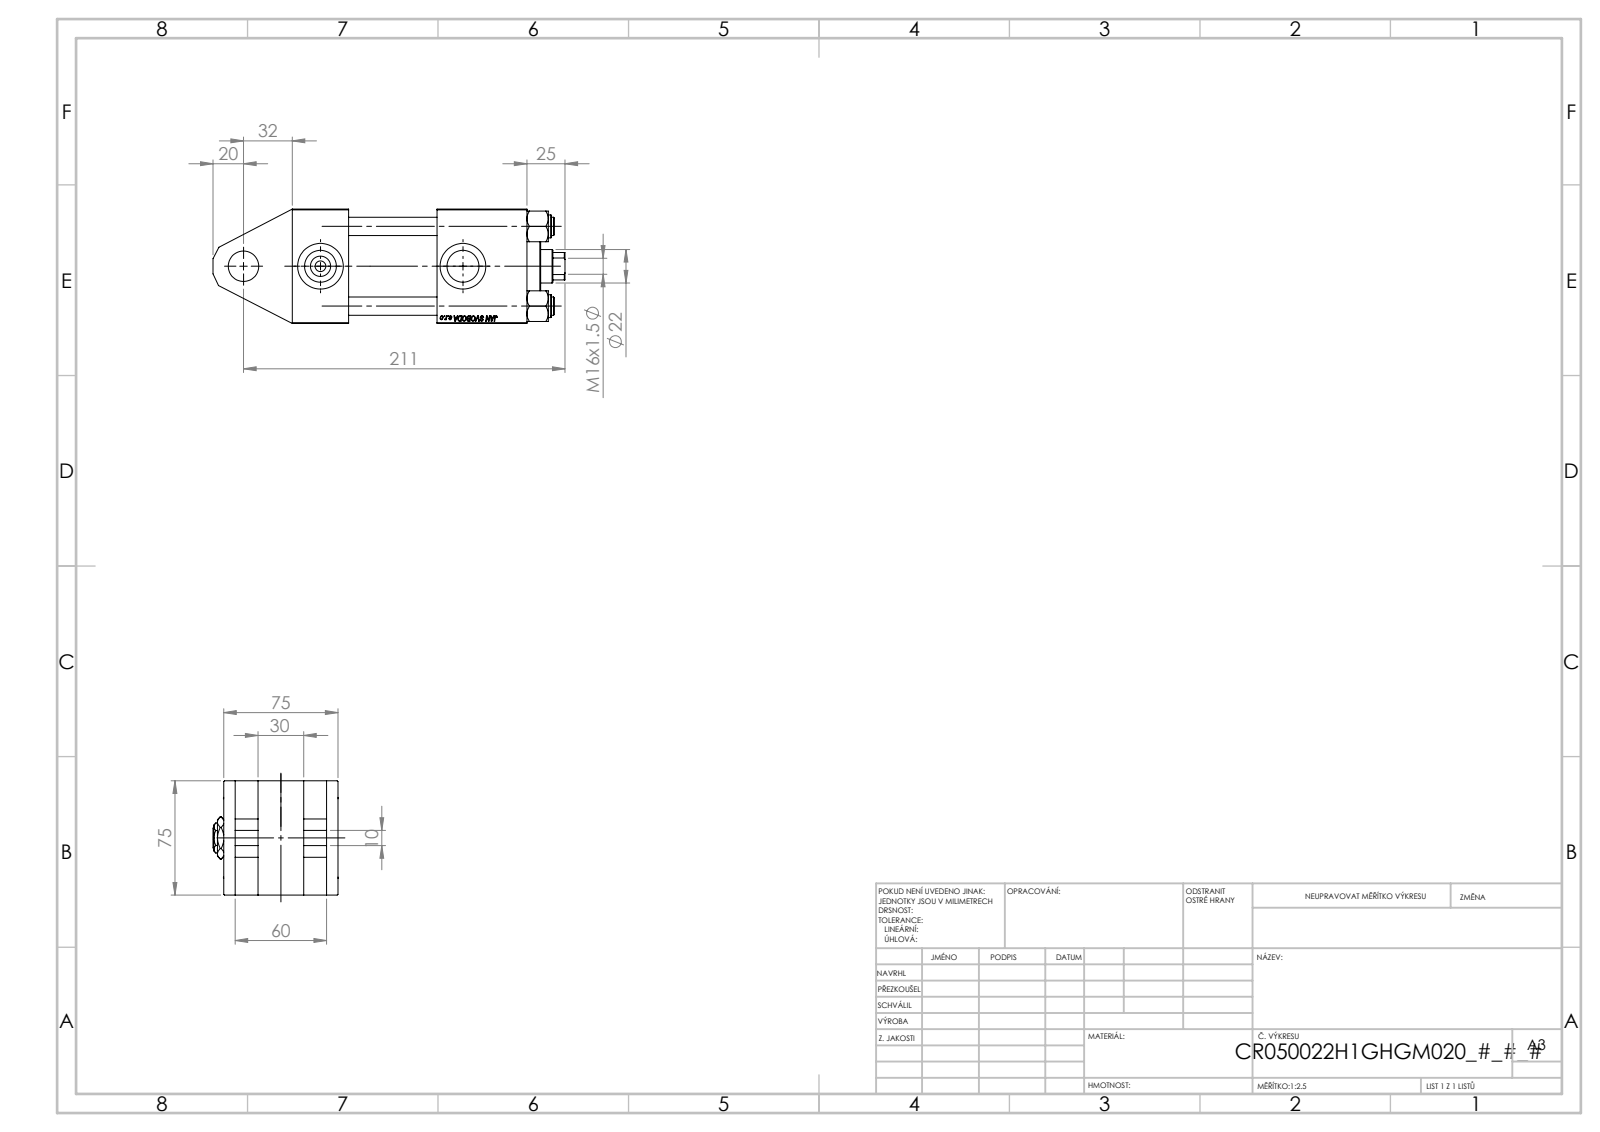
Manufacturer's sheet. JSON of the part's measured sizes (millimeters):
{"part_name": "V215_VC_A; V215CR_VCP_H; V215CR_H_Body; Zatka_pro_OIL_PORT (+2 more)", "step_written_by": "SolidWorks 2019 (CONFIG_CONTROL_DESIGN)", "units": "millimeters", "bodies": {"solids": 12, "faces": 1176, "planar": 541, "cylindrical": 87, "other": 548}, "overall_size": [231, 82.27, 75], "volume_mm3": 730736, "surface_area_mm2": 164839, "round_holes": [[12, 4], [7, 2], [20.96, 2], [30, 2], [10.5, 1], [20, 1], [22, 1], [25, 1], [41, 1], [50, 1], [53, 1]], "round_bosses_or_shafts": [[15, 4], [56, 1], [34, 1]], "partial_cylinders_radius": [[10.5, 1]], "face_to_face_distances": [75, 117, 67.5, 7.5, 45, 22.5, 52.5, 15, 95, 37], "hole_center_spacings": [36.98, 52.3, 73.96, 50.5, 93.5, 144]}
